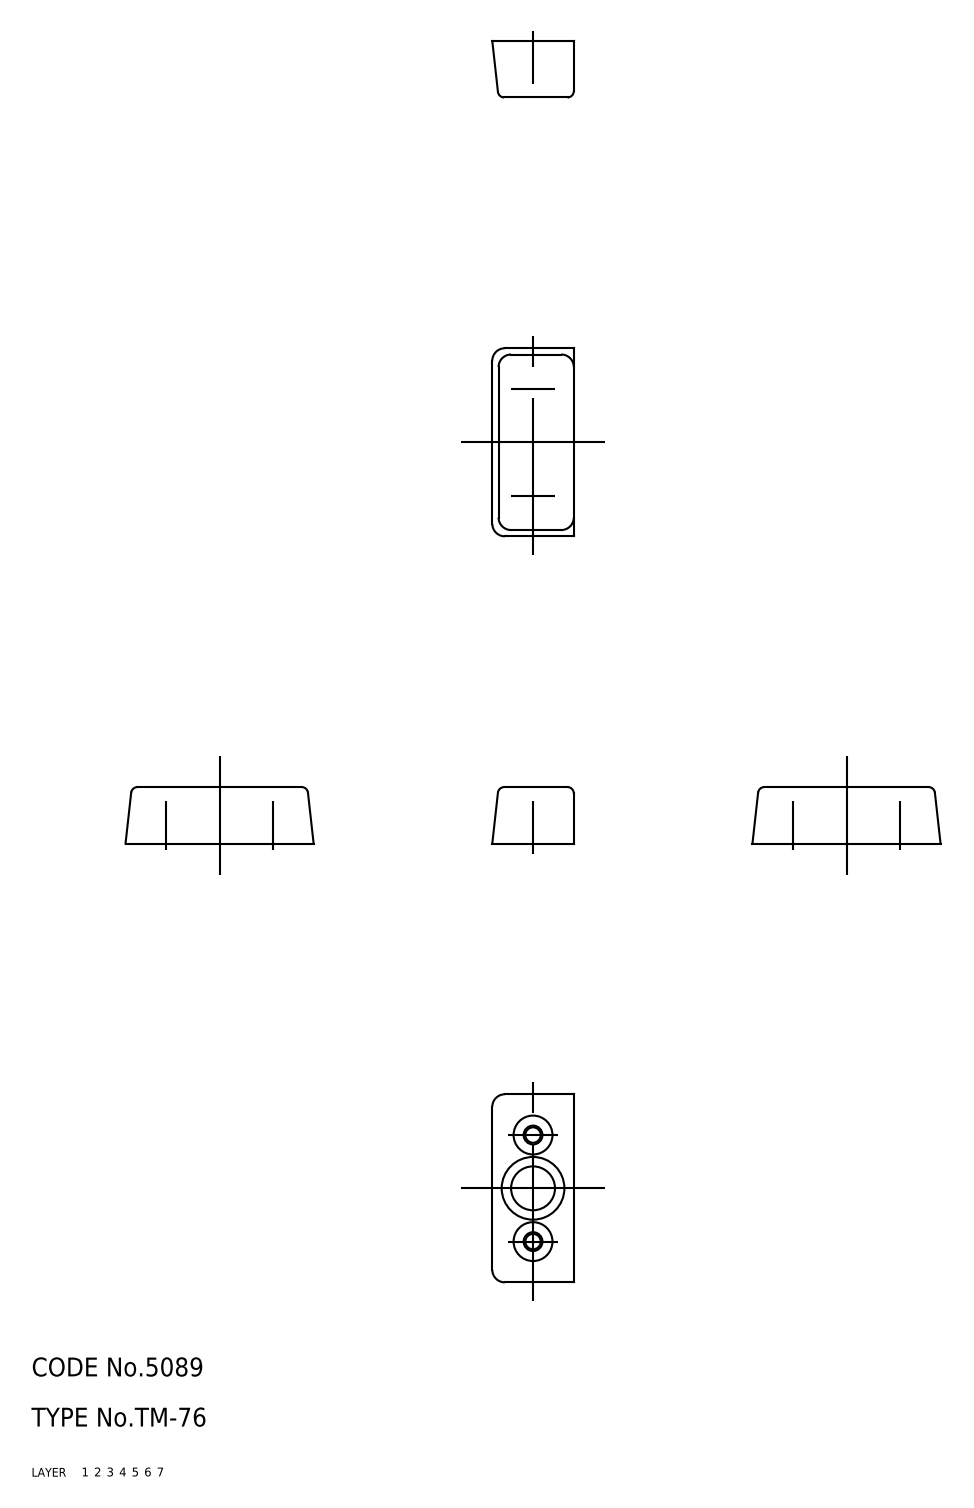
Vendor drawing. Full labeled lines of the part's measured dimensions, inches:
Part name (STEP PRODUCT): rubber pad
STEP written by: CADfix (AUTOMOTIVE_DESIGN)
Units: inches
Bodies: 1 solid, 25 faces (0 planar, 0 cylindrical, 25 other)
Overall size (bounding box): 1.181 × 0.512 × 0.354
Volume: 0.186 in³ · Surface area: 2.461 in²
